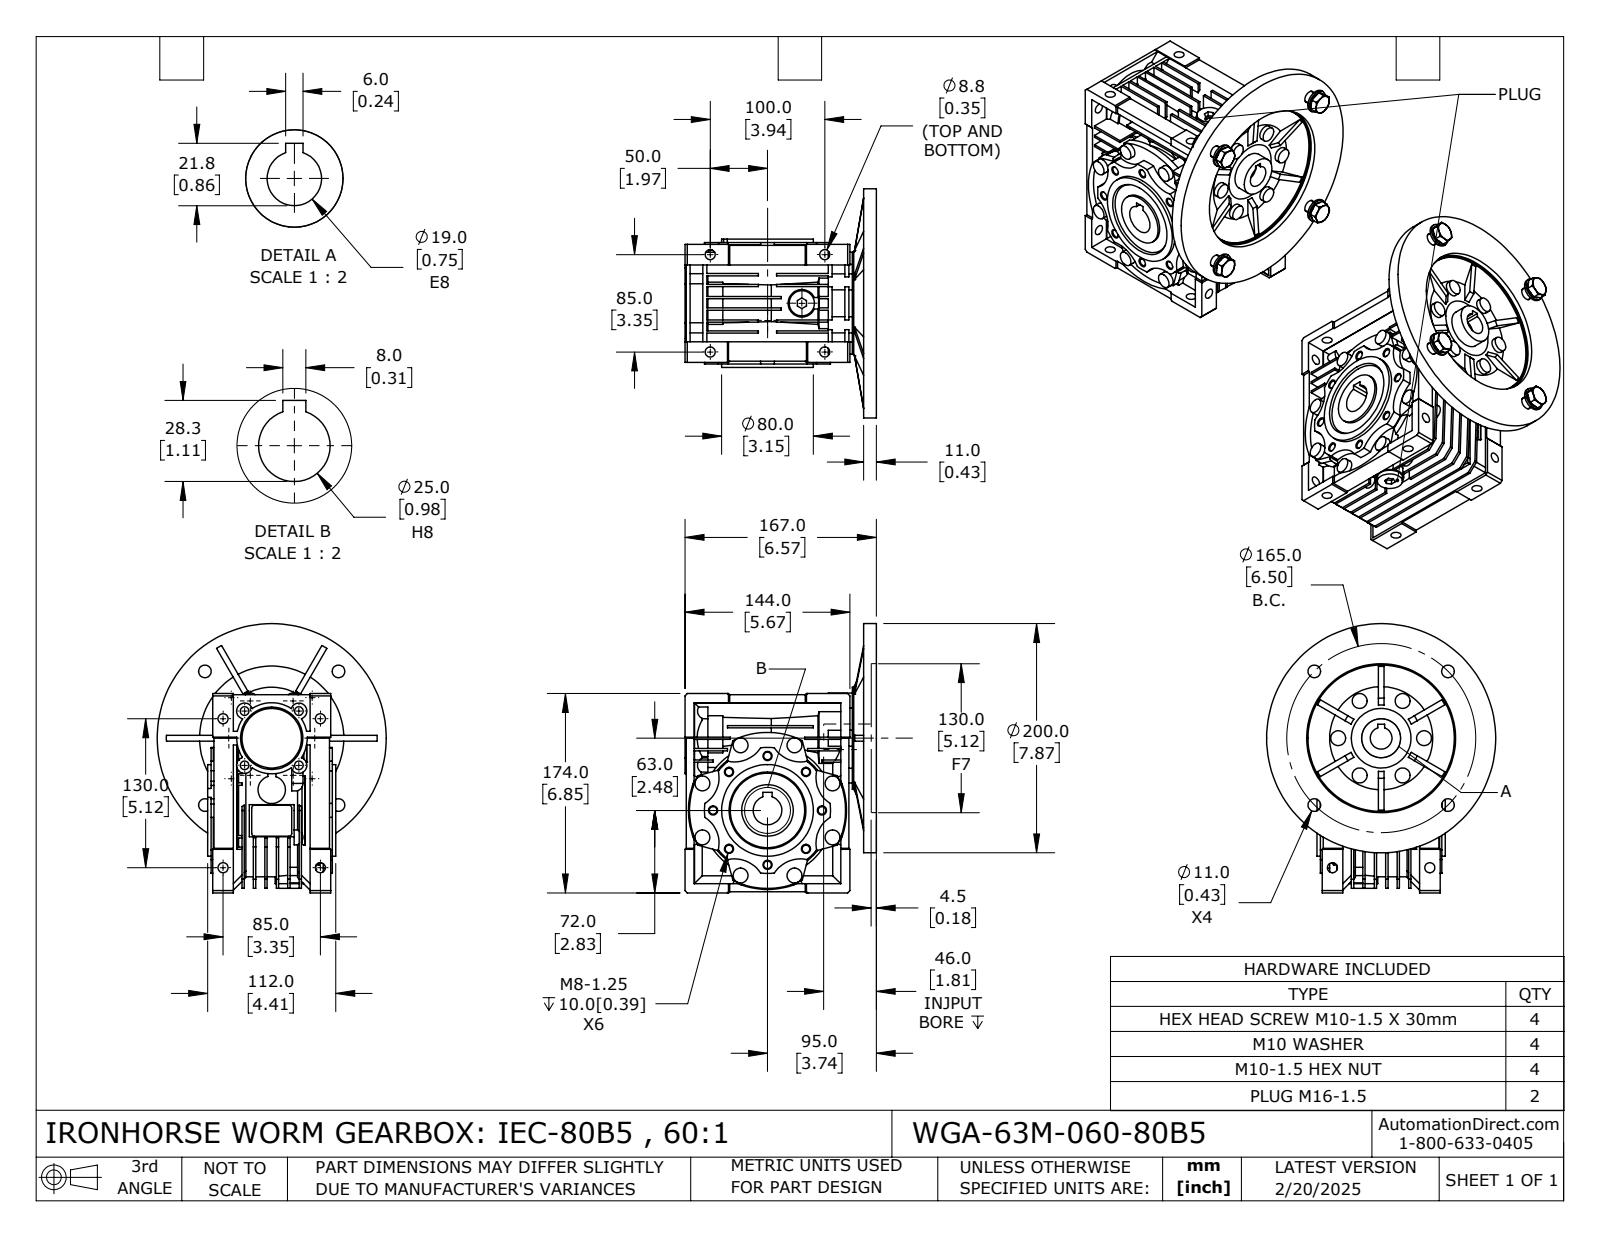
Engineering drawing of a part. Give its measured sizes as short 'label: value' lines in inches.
name: WGA-63M-060-80B5
written by: SolidWorks 2024 (CONFIG_CONTROL_DESIGN)
unit: in
bodies: 20 solids, 1529 faces (897 planar, 394 cylindrical, 238 other)
size: 9.252 × 7.874 × 7.222
volume: 124 in³; area: 622.2 in²
holes: 8× ⌀0.262, 8× ⌀0.346, 4× ⌀0.298, 4× ⌀0.335, 4× ⌀0.394, 4× ⌀0.413, 4× ⌀0.433, 2× ⌀0.571, 1× ⌀0.748, 1× ⌀0.787, 1× ⌀0.984, 1× ⌀1.339
bosses: 14× ⌀0.512, 4× ⌀0.787, 4× ⌀0.63, 3× ⌀0.945, 2× ⌀0.866, 2× ⌀0.622, 2× ⌀0.539, 1× ⌀7.874
rounds: 10× R0.276, 8× R1.063, 4× R0.098, 1× R0.329, 1× R1.161, 1× R1.201, 1× R1.654, 1× R1.811
face distances: 0.394, 0.315, 0.787, 0.079, 0.433, 1.181, 0.472, 0.276, 1.575, 0.709
hole spacings: 1.431, 1.87, 2.645, 3.456, 3.506, 1.319, 1.865, 1.929
